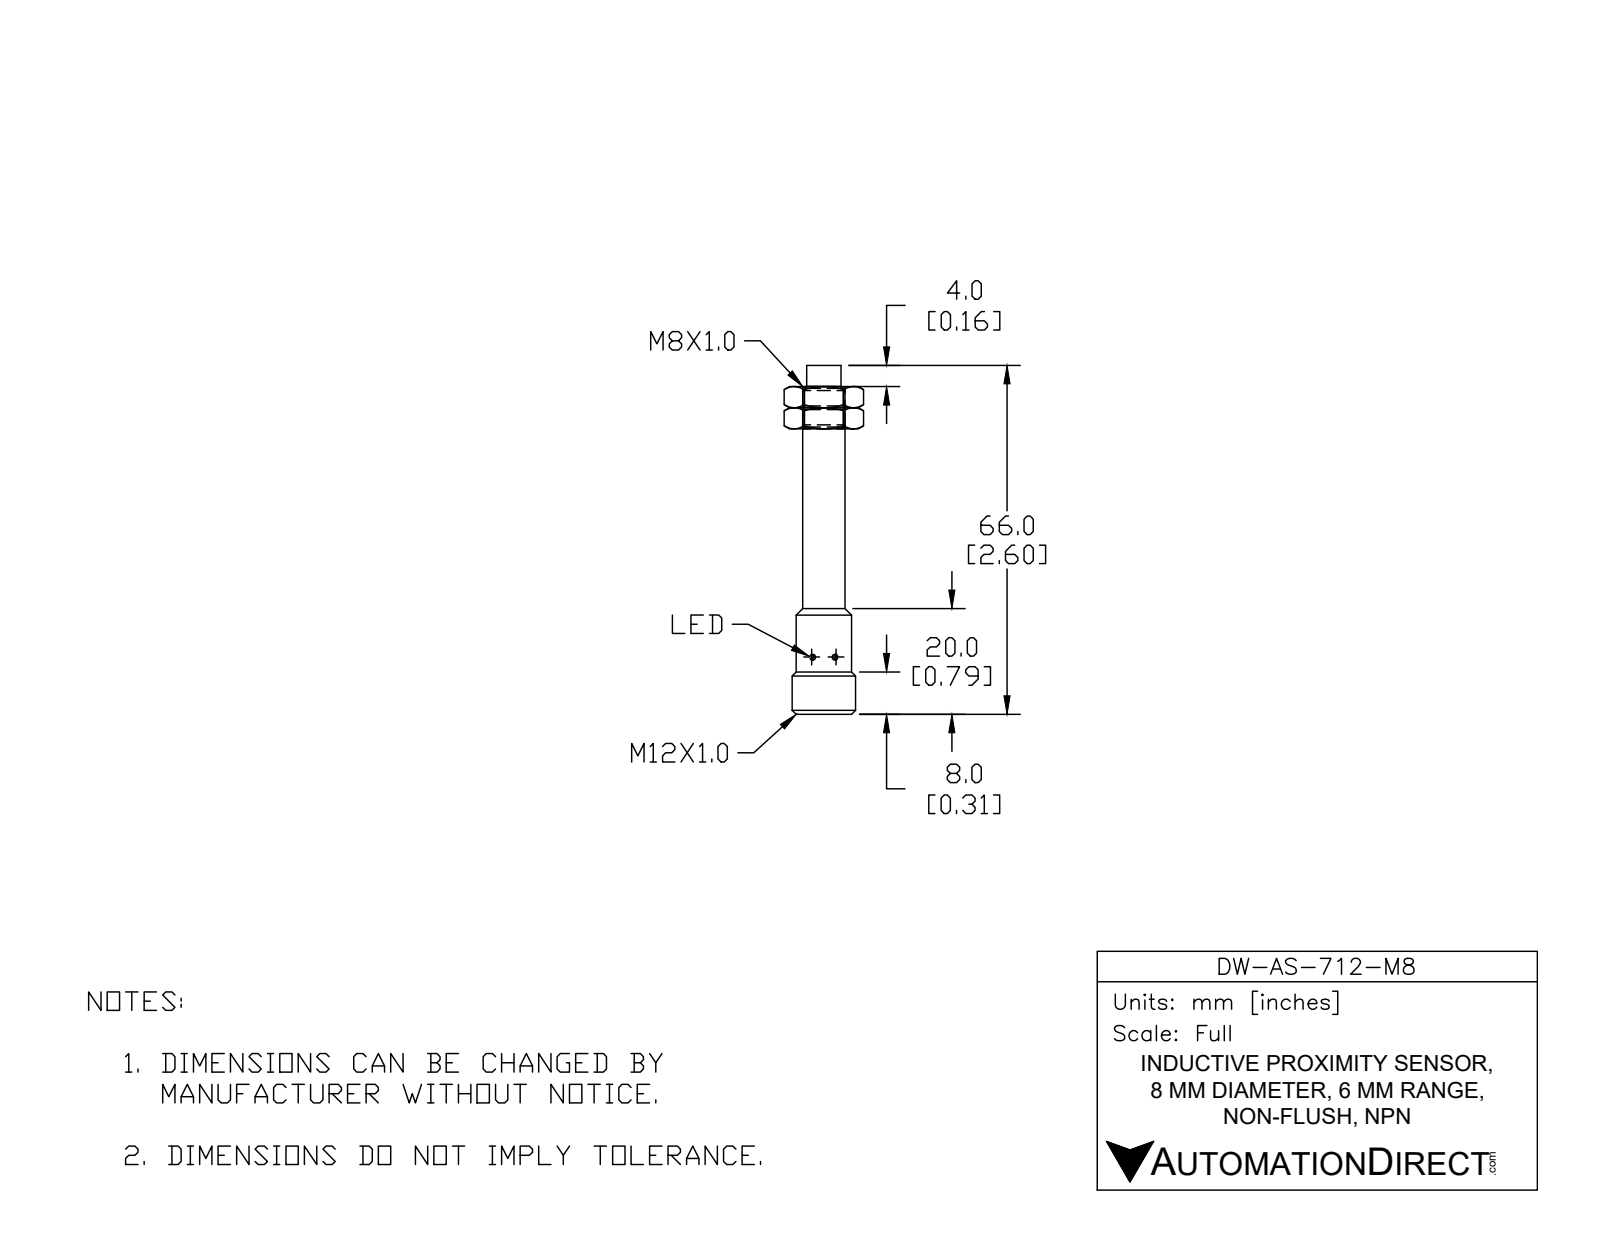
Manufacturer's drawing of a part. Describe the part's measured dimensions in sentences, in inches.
The part is named "DW-AS-712-M8". Its 3-D file was written by "SolidWorks 2017 (AUTOMOTIVE_DESIGN)". It is 1 solid with 43 faces: 7 planar, 26 cylindrical and 10 other. Overall it measures 2.598 by 0.472 by 0.472 inches. Its volume is 0.218 cubic inches and its surface area 3.895 square inches. Round holes: 2 of diameter 0.118, 1 of diameter 0.335. Round bosses or shafts: 4 of diameter 0.039, 1 of diameter 0.472, 1 of diameter 0.415, 1 of diameter 0.315, 1 of diameter 0.256. Partial cylindrical surfaces (rounded edges, fillets, slot ends): 2 of radius 0.02, 1 of radius 0.022, 1 of radius 0.183, 1 of radius 0.193. The main face-to-face distances are 0.343, 2.256, 2.598, 1.811, 0.445, 0.787, 0.043, 2.539, 0.728, 0.283.
